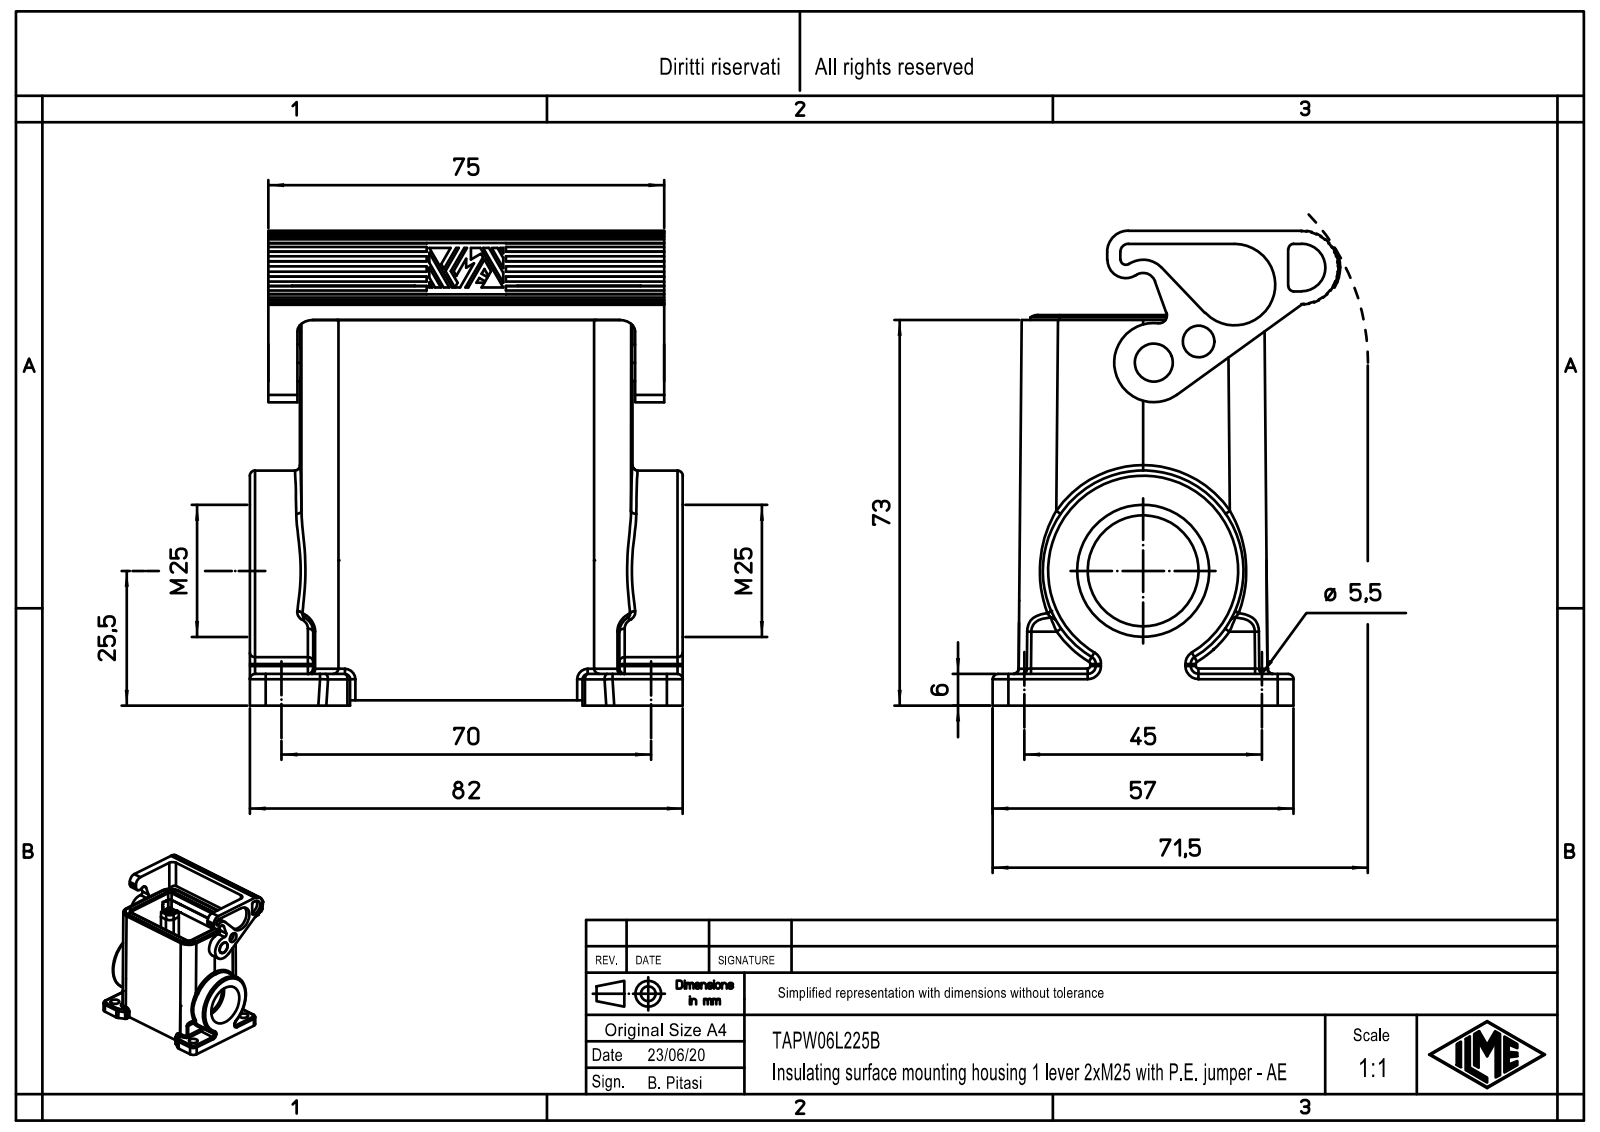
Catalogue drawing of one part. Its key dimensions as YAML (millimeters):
part_name: "TAPW06L225B"
step_written_by: "Creo Elements/Direct Modeling 20.1B 02-Apr-2019 (C) Parametric Technology GmbH (AUTOMOTIVE_DESIGN)"
units: millimeters
bodies: {solids: 1, faces: 780, planar: 399, cylindrical: 227, other: 154}
overall_size: [89.9, 82, 65.8]
volume: 139354
surface_area: 50036
round_holes:
  - {diameter: 3, count: 4}
  - {diameter: 3.5, count: 4}
  - {diameter: 5.5, count: 4}
  - {diameter: 6, count: 1}
  - {diameter: 10, count: 1}
  - {diameter: 21, count: 1}
  - {diameter: 25, count: 1}
round_bosses_or_shafts:
  - {diameter: 4.8, count: 4}
  - {diameter: 38, count: 1}
  - {diameter: 7, count: 1}
partial_cylinders:
  - {radius: 1, count: 32}
  - {radius: 1.5, count: 18}
  - {radius: 3, count: 12}
  - {radius: 3.5, count: 5}
  - {radius: 7, count: 5}
  - {radius: 0.5, count: 4}
  - {radius: 1.3, count: 4}
  - {radius: 1.6, count: 4}
face_to_face_distances: [40.6, 5.5, 73, 1, 6, 9, 6.5, 67, 0.5, 5]
hole_center_spacings: [15.81, 38.28, 57.71, 67.42, 27, 44, 45, 51.62]
